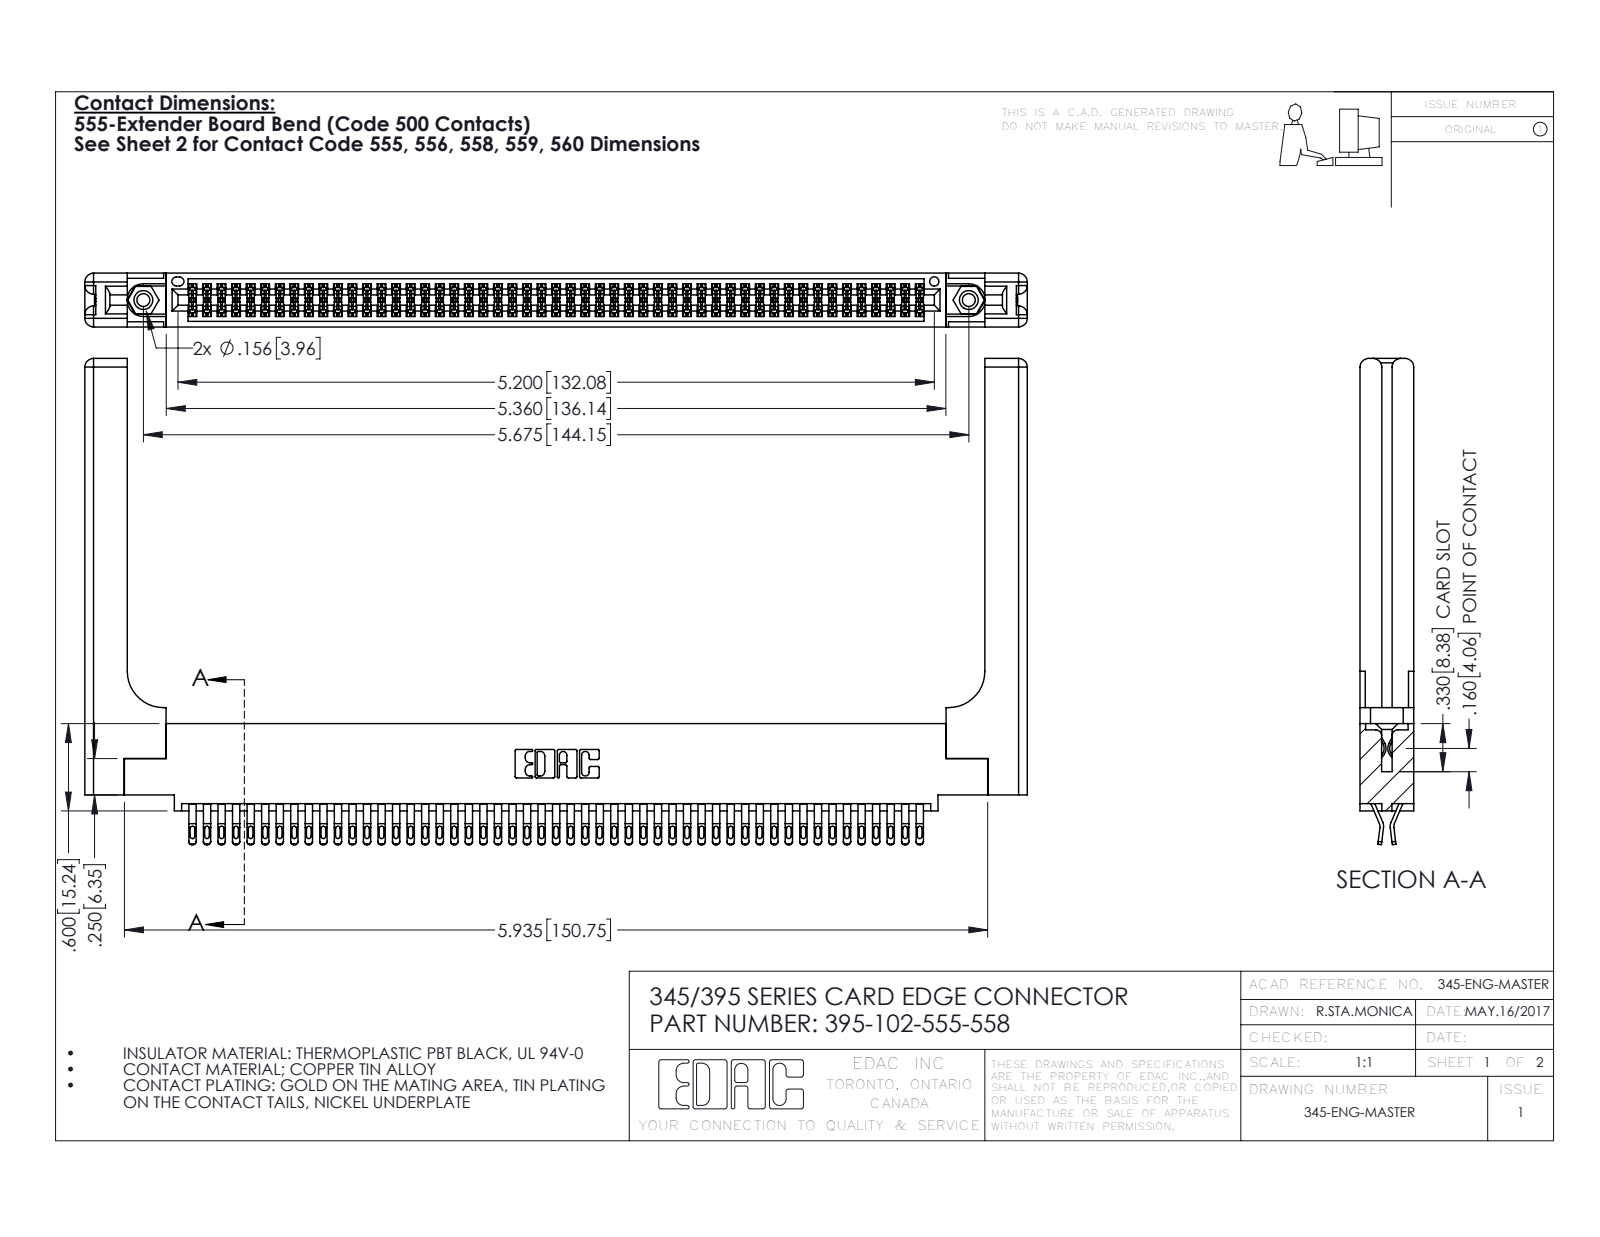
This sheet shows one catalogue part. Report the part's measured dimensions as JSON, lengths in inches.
{"part_name": "345-220-058_345-220-058; 345-250-001_345-250-001-102; 345-292-001_555 Tail; 395-102-555-558 (+1 more)", "step_written_by": "SolidWorks 2016 (CONFIG_CONTROL_DESIGN)", "units": "inches", "bodies": {"solids": 107, "faces": 6098, "planar": 3394, "cylindrical": 2644, "other": 60}, "overall_size": [6.479, 3.342, 0.37], "volume_in3": 1.511, "surface_area_in2": 47.18, "round_holes": [[0.089, 2], [0.125, 2], [0.156, 2], [0.064, 1]], "round_bosses_or_shafts": [[0.155, 2]], "partial_cylinders_radius": [[0.016, 255], [0.02, 204], [0.006, 153], [0.01, 22], [0.06, 16], [0.007, 6], [0.031, 6], [0.026, 3]], "face_to_face_distances": [0.072, 0.298, 0.37, 0.025, 0.098, 0.272, 0.2, 0.225, 0.148, 0.15], "hole_center_spacings": [0.27, 5.439, 5.675]}
